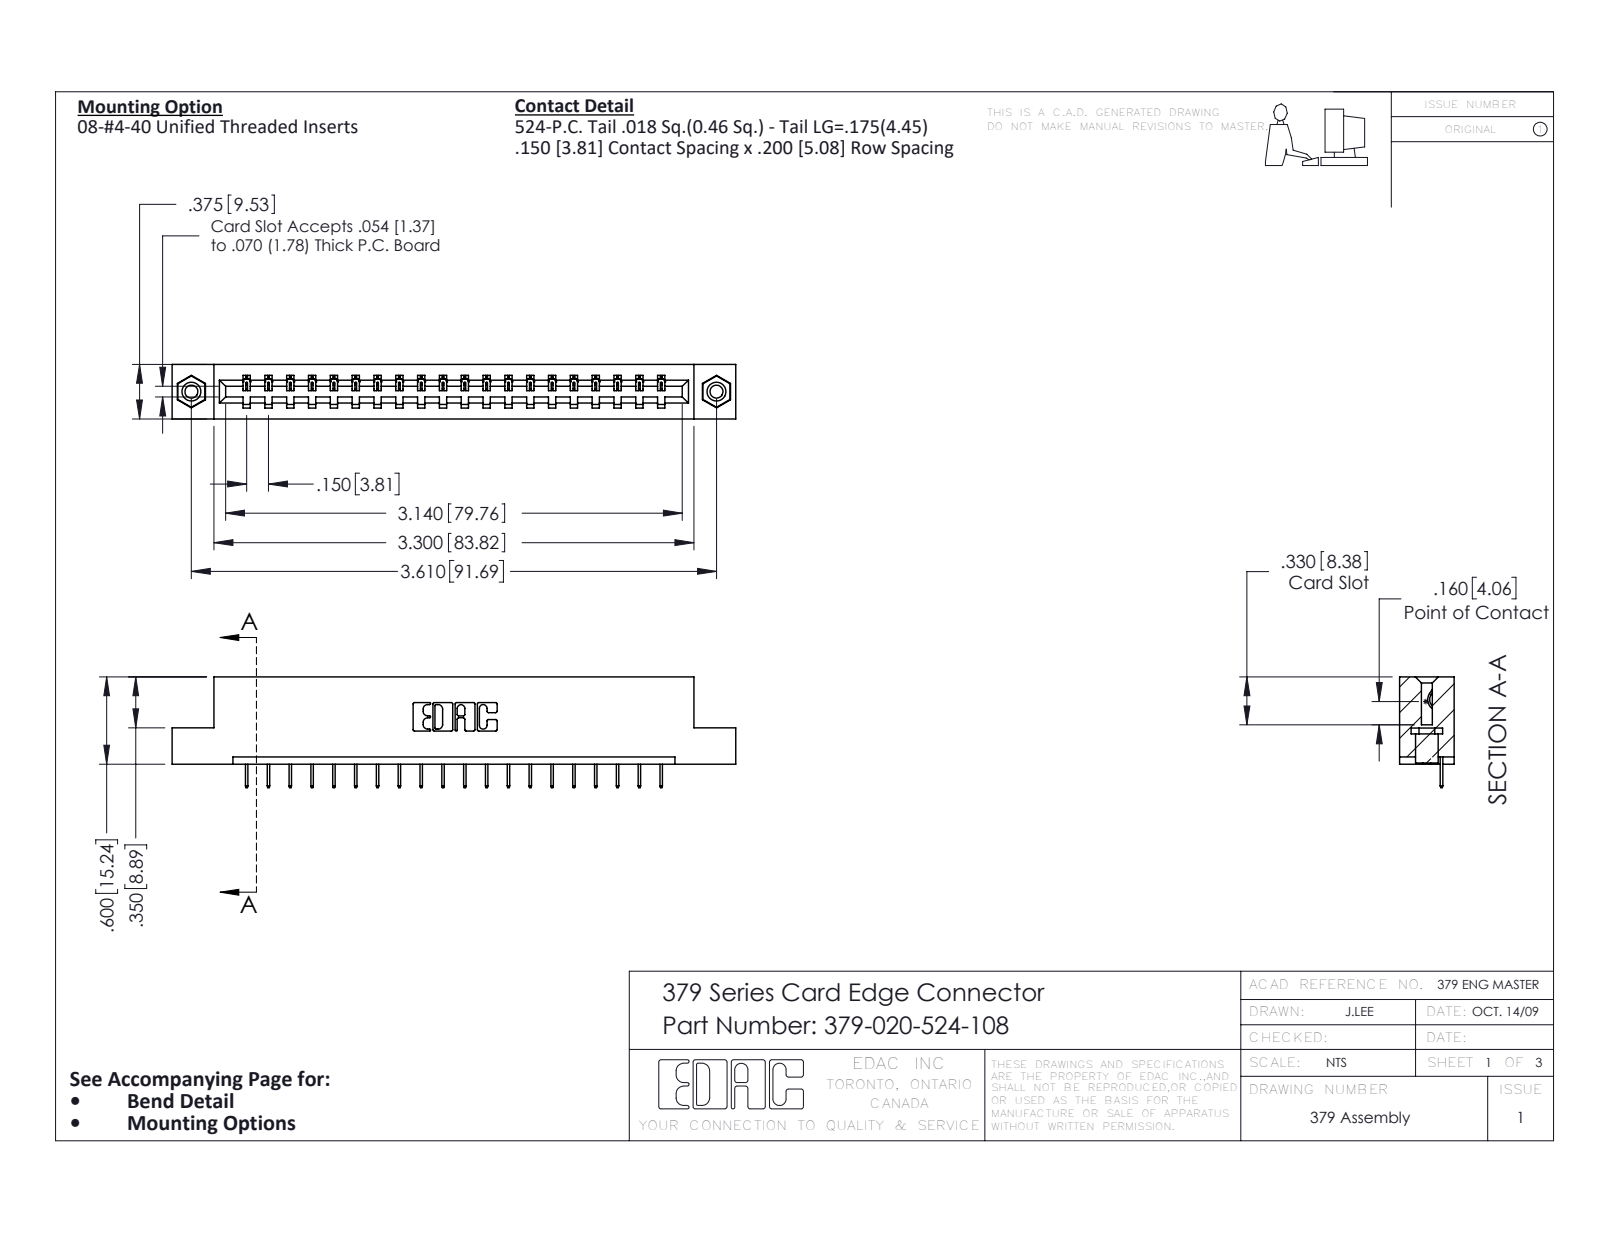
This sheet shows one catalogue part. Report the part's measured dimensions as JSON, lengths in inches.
{"part_name": "345-250-001_345-250-003-102; 379 Part_Flush - .156 Dia - TI; 379-020-524-108; 345-292-001_345-293-124", "step_written_by": "SolidWorks 2016 (CONFIG_CONTROL_DESIGN)", "units": "inches", "bodies": {"solids": 23, "faces": 1414, "planar": 1062, "cylindrical": 336, "other": 16}, "overall_size": [3.875, 0.762, 0.375], "volume_in3": 0.61, "surface_area_in2": 15.29, "round_holes": [[0.089, 2], [0.125, 2], [0.156, 2]], "round_bosses_or_shafts": [[0.155, 2]], "partial_cylinders_radius": [[0.006, 40], [0.01, 22], [0.007, 6], [0.031, 6], [0.026, 3], [0.014, 1], [0.022, 1], [0.024, 1]], "face_to_face_distances": [0.3, 0.375, 0.075, 0.6, 0.225, 0.15, 0.45, 0.75, 0.55, 0.2], "hole_center_spacings": [3.61]}
